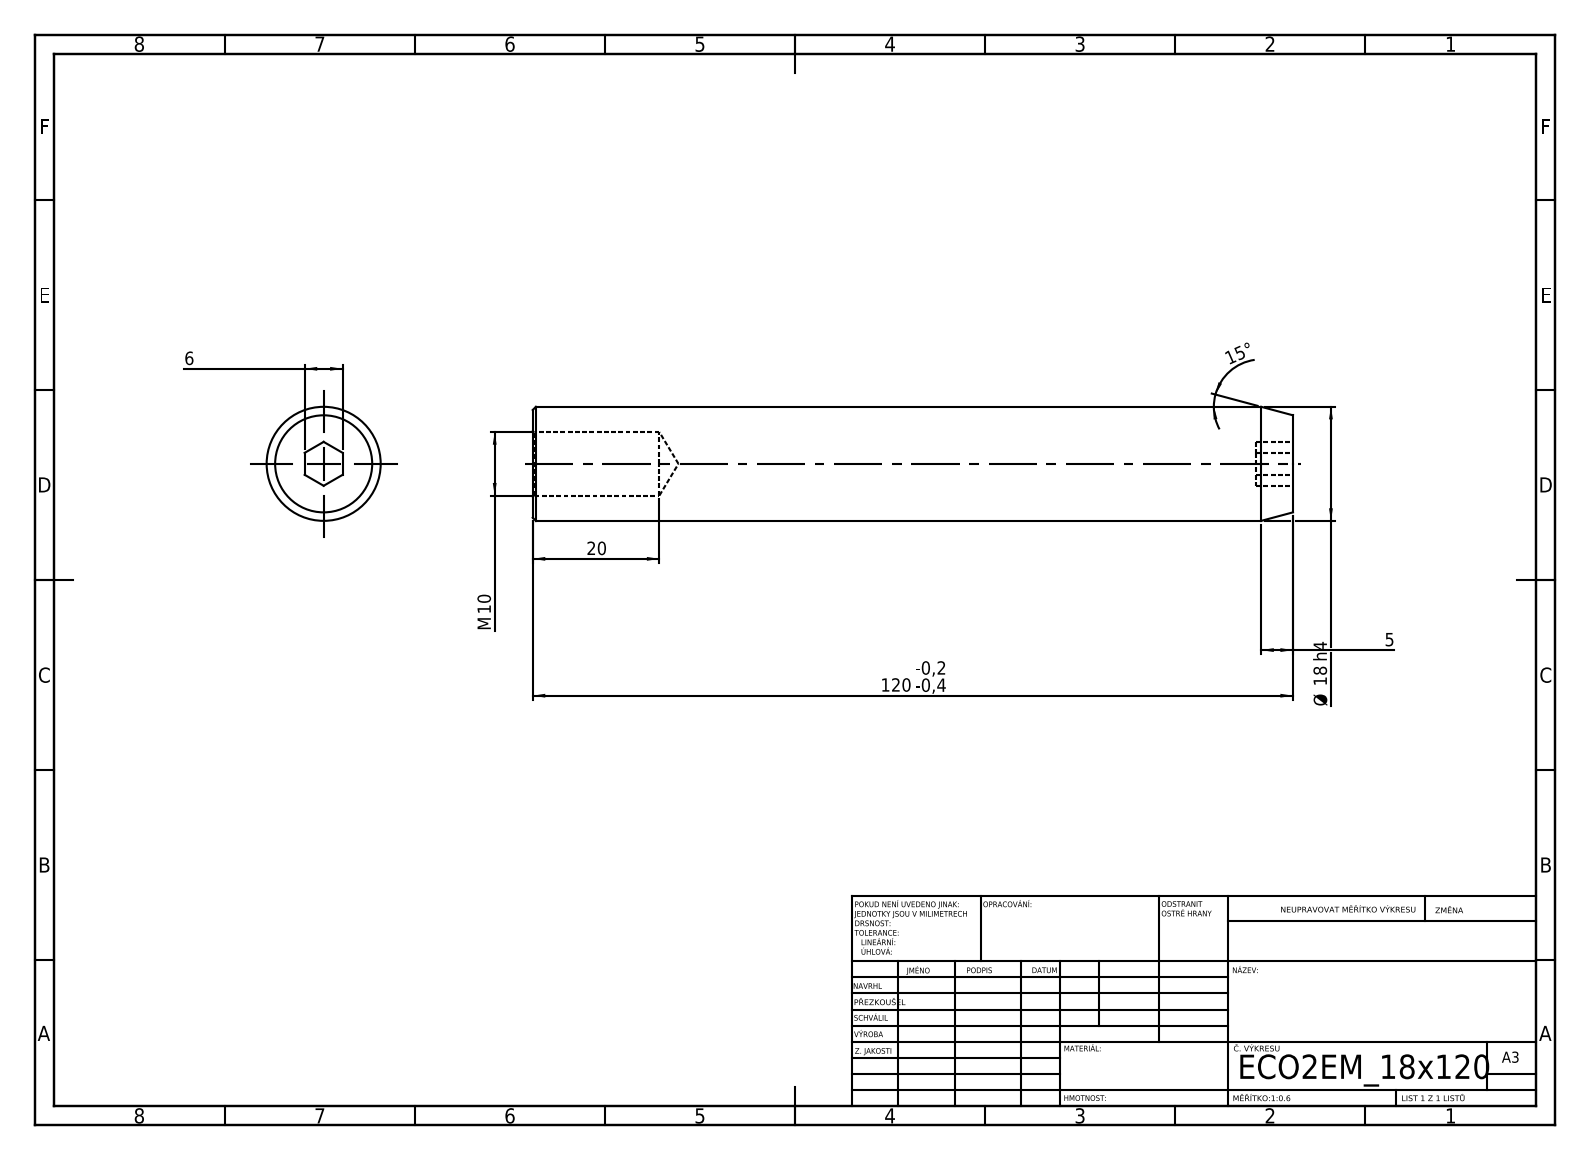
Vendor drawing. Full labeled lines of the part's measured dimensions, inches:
STEP written by: SolidWorks 2019 (CONFIG_CONTROL_DESIGN)
Units: inches
Bodies: 1 solid, 21 faces (9 planar, 4 cylindrical, 8 other)
Overall size (bounding box): 4.724 × 0.709 × 0.709
Volume: 1.74 in³ · Surface area: 12.33 in²
Round holes (diameter × count): ⌀0.394 ×1
Round bosses / shafts (diameter × count): ⌀0.709 ×1
Main face-to-face distances: 4.724, 0.236, 0.228, 4.496
